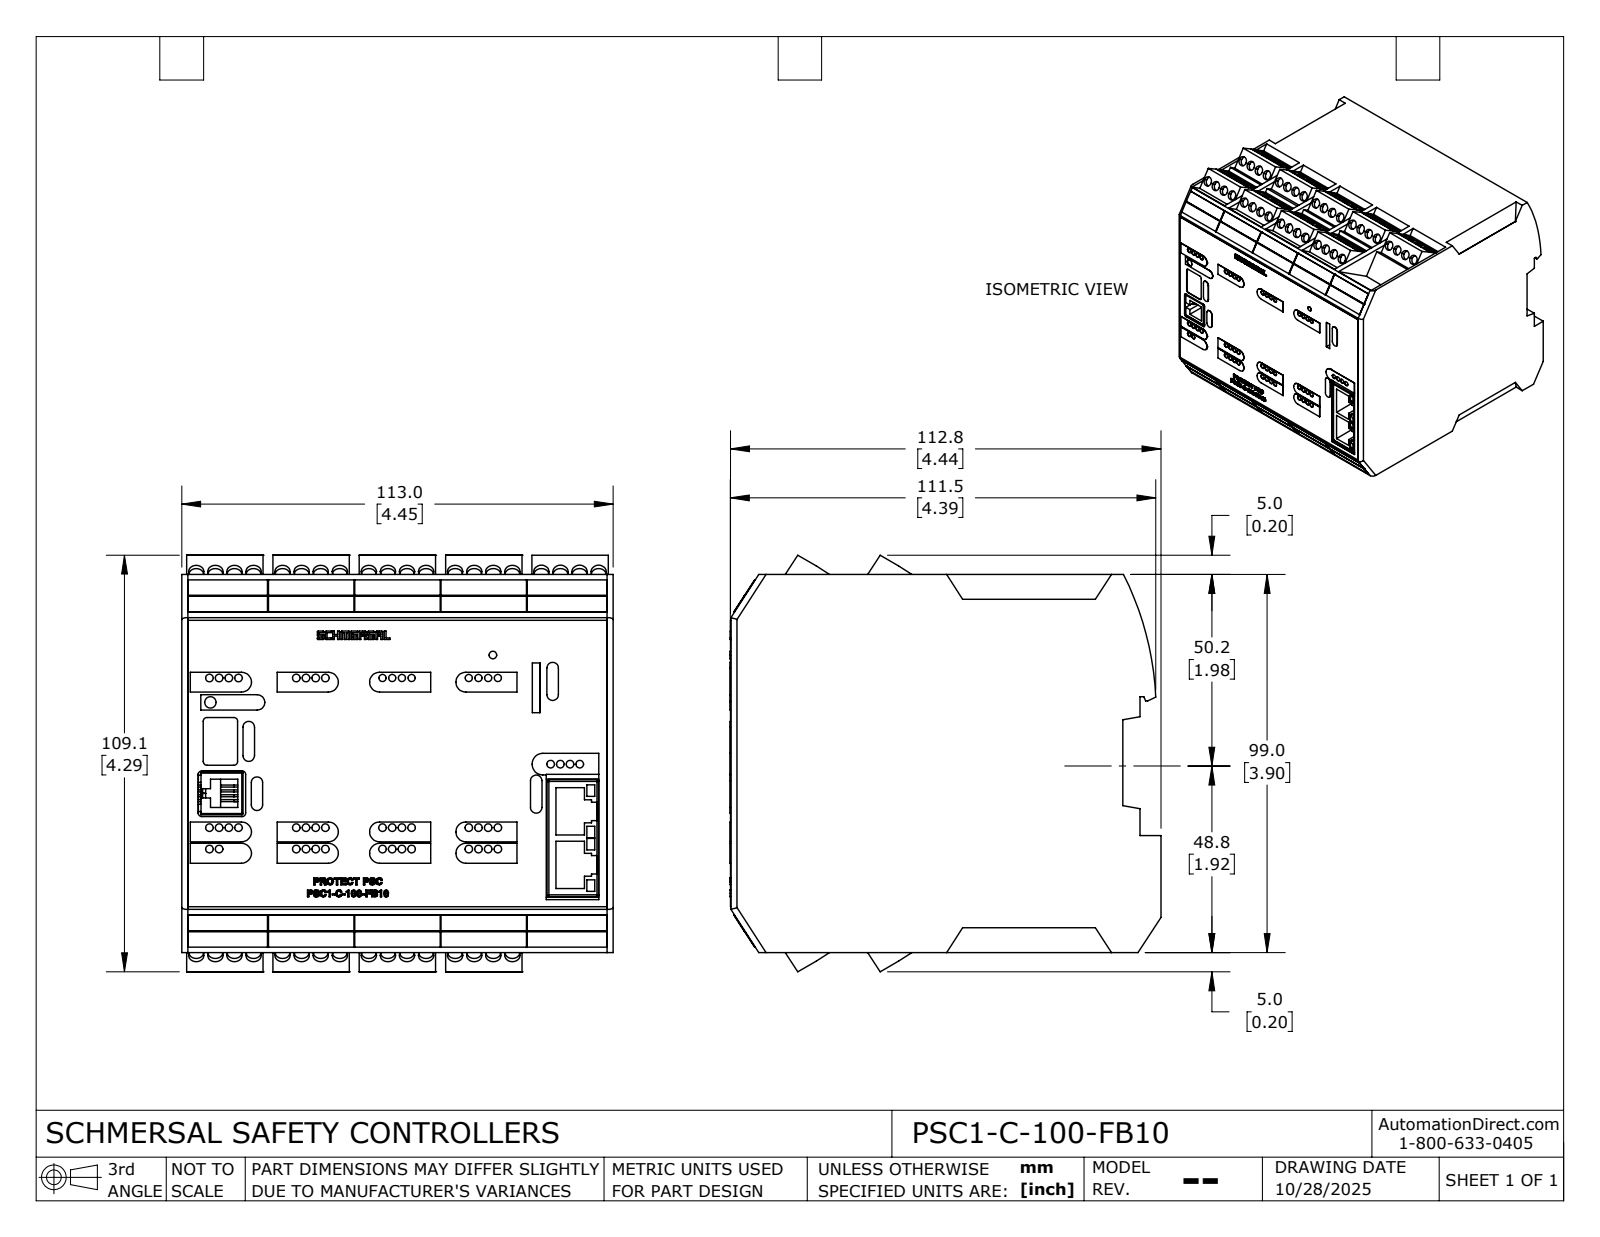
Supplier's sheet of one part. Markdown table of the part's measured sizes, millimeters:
| quantity | value |
| --- | --- |
| part name | PSC1-C-100-FB10 |
| STEP written by | SolidWorks 2024 (AUTOMOTIVE_DESIGN) |
| units | millimeters |
| bodies | 1 solid, 1935 faces (1177 planar, 363 cylindrical, 395 other) |
| overall size | 113 × 112.85 × 109.09 |
| volume | 1 178 000 mm³ |
| surface area | 92 582 mm² |
| round holes (diameter × count) | 4 × 68, 2 × 42, 1.89 × 8, 3 × 1 |
| round bosses / shafts (diameter × count) | 2 × 1 |
| partial cylindrical surfaces (radius × count) | 2.6 × 12, 1 × 10, 1.5 × 10, 0.3 × 8, 0.45 × 8, 1.6 × 6, 0.7 × 4, 0.2 × 2 |
| main face-to-face distances | 113, 22.6, 99, 45.2, 2.55, 22.55, 20.05, 22.65, 42.65, 67.8 |
| hole center spacings | 22.6, 25.48, 5, 12.78, 17.6, 21.17, 27.6, 30 |
